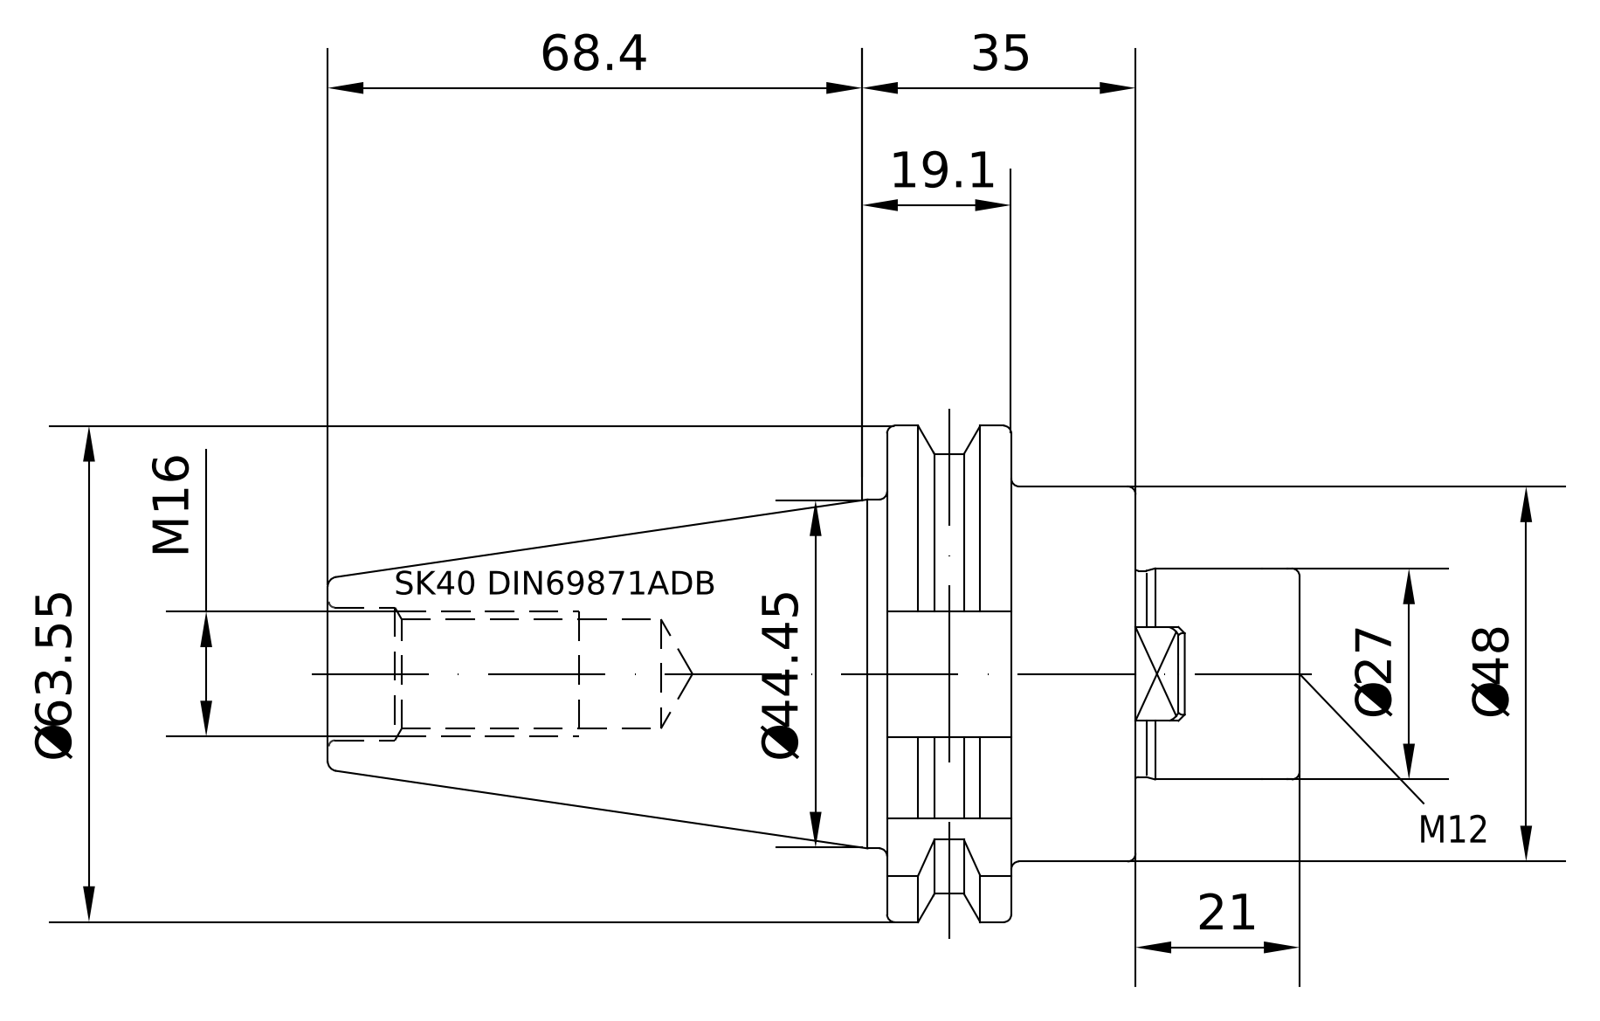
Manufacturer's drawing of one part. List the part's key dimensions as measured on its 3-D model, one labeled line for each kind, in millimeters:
Part name (STEP PRODUCT): 40-350-27
STEP written by: PRO/ENGINEER BY PARAMETRIC TECHNOLOGY CORPORATION, 2010430 (CONFIG_CONTROL_DESIGN)
Units: millimetres
Bodies: 1 solid, 121 faces (40 planar, 32 cylindrical, 49 other)
Overall size (bounding box): 124.25 × 63.52 × 61.42
Volume: 144 909 mm³ · Surface area: 26 627 mm²
Round holes (diameter × count): ⌀10.2 ×1, ⌀12 ×1, ⌀13.84 ×1, ⌀17.01 ×1, ⌀17.5 ×1
Round bosses / shafts (diameter × count): ⌀48 ×1, ⌀43.75 ×1, ⌀27 ×1, ⌀16.01 ×1
Partial cylindrical surfaces — rounded edges, fillets, slot ends (radius × count): R1.35 ×5, R28 ×1, R31.76 ×1
Main face-to-face distances: 31.8, 15.85, 15.95, 52.8, 36.95, 21, 2.1, 14.1, 47.4, 38.1
